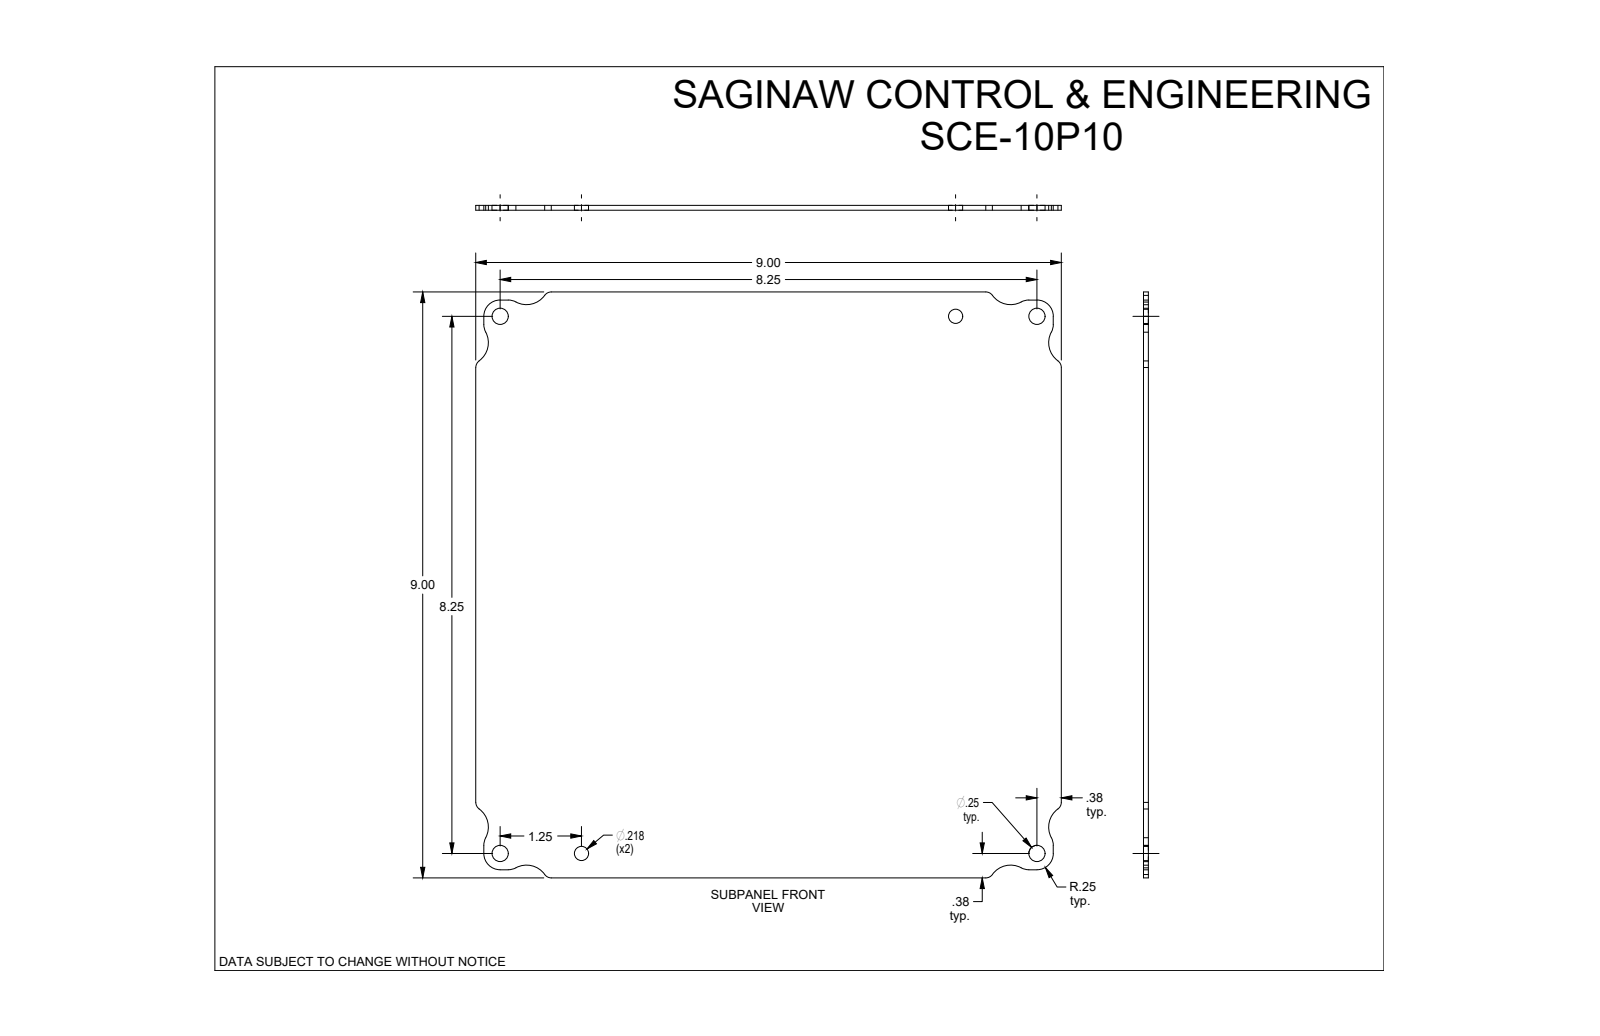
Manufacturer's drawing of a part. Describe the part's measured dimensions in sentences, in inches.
The part is named "SCE-10P10". Its 3-D file was written by "SolidWorks 2019 (CONFIG_CONTROL_DESIGN)". It is 1 solid with 48 faces: 14 planar, 34 cylindrical and 0 other. Overall it measures 9 by 9 by 0.075 inches. Its volume is 5.964 cubic inches and its surface area 162 square inches. Round holes: 4 of diameter 0.25, 2 of diameter 0.218. Partial cylindrical surfaces (rounded edges, fillets, slot ends): 12 of radius 0.25, 8 of radius 0.125, 8 of radius 0.344. The main face-to-face distances are 0.075, 9, 0.125, 8.875, 0.124, 8.876, 8.75, 8.752. The hole center spacings are 8.25, 1.25, 7, 8.344, 10.819, 11.667, 10.056.
